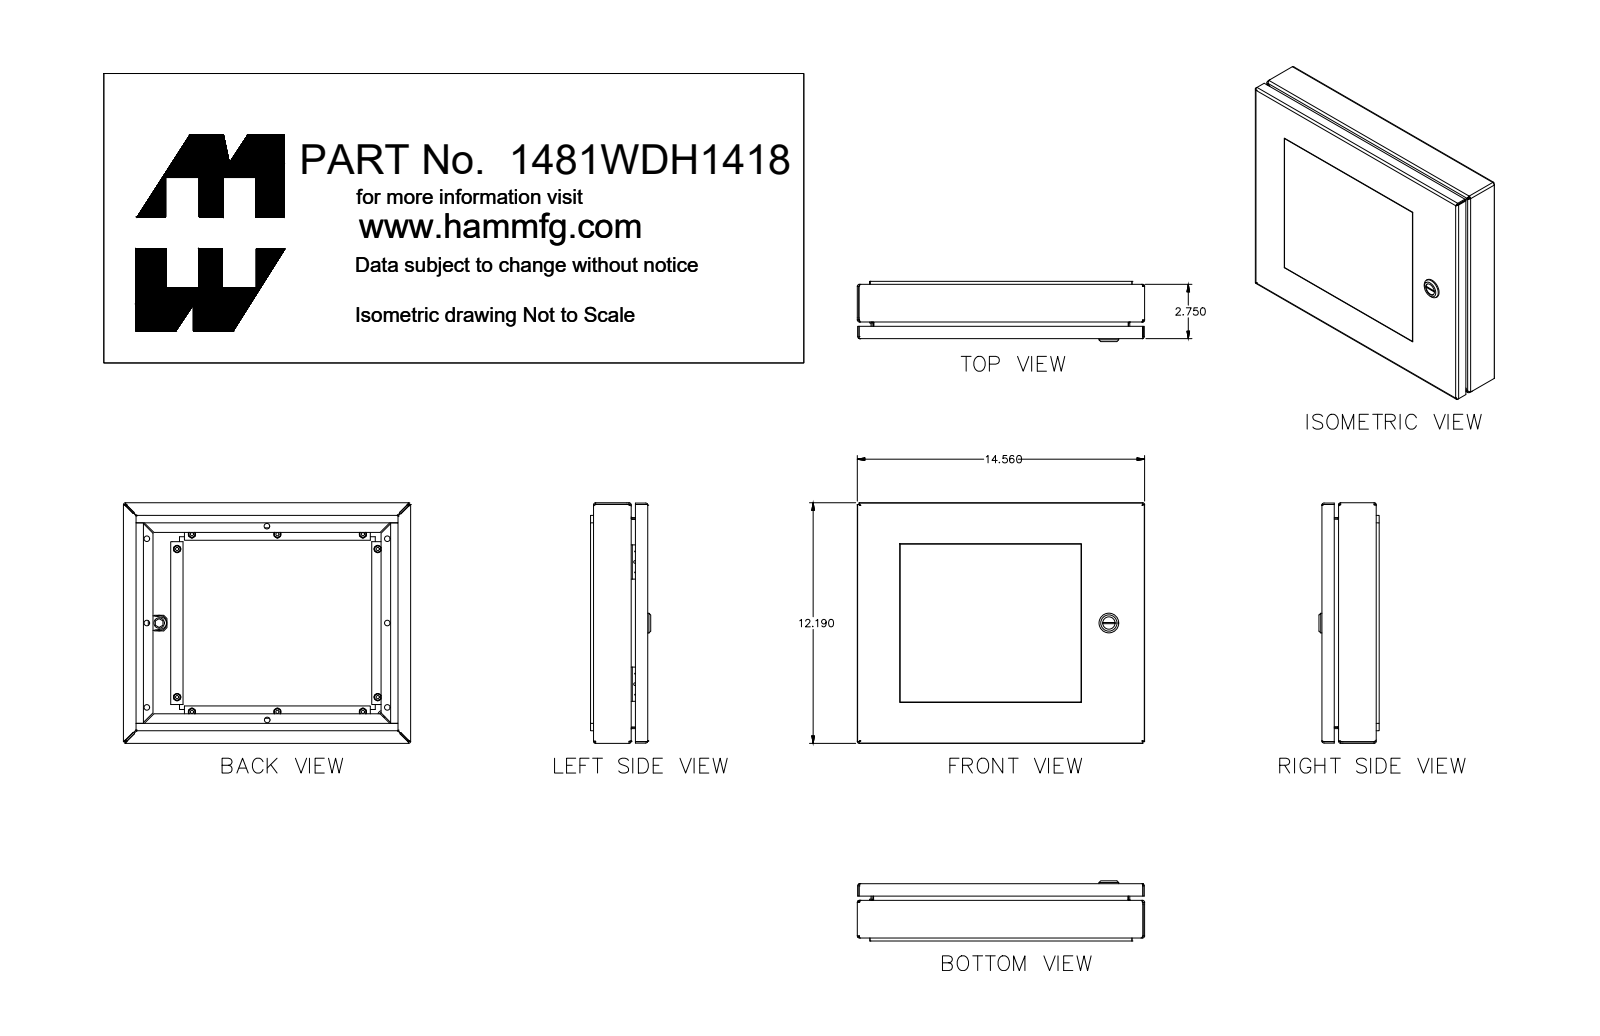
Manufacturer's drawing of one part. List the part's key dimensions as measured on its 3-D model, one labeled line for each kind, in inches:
Part name (STEP PRODUCT): 1481WDH1418_Default
STEP written by: SolidWorks 2019 (CONFIG_CONTROL_DESIGN)
Units: inches
Bodies: 41 solids, 984 faces (531 planar, 275 cylindrical, 178 other)
Overall size (bounding box): 14.56 × 12.19 × 2.91
Volume: 49.39 in³ · Surface area: 1 025 in²
Round holes (diameter × count): ⌀0.13 ×10, ⌀0.281 ×8, ⌀0.136 ×2, ⌀0.232 ×1, ⌀0.24 ×1, ⌀0.242 ×1, ⌀0.625 ×1, ⌀0.785 ×1
Round bosses / shafts (diameter × count): ⌀0.368 ×10, ⌀0.226 ×10, ⌀0.164 ×10, ⌀1.1 ×1, ⌀0.525 ×1, ⌀0.455 ×1, ⌀0.398 ×1, ⌀0.356 ×1
Partial cylindrical surfaces — rounded edges, fillets, slot ends (radius × count): R0.036 ×28, R0.108 ×28, R0.101 ×20, R0.016 ×4, R0.088 ×4, R0.125 ×2, R0.021 ×1, R0.029 ×1
Main face-to-face distances: 0.072, 0.25, 0.178, 2.578, 0.842, 1.736, 2.328, 0.592, 12.118, 14.488
Hole centre spacings: 4.335, 6.125, 7.822, 9.45, 9.99, 11.017, 12.912, 9
